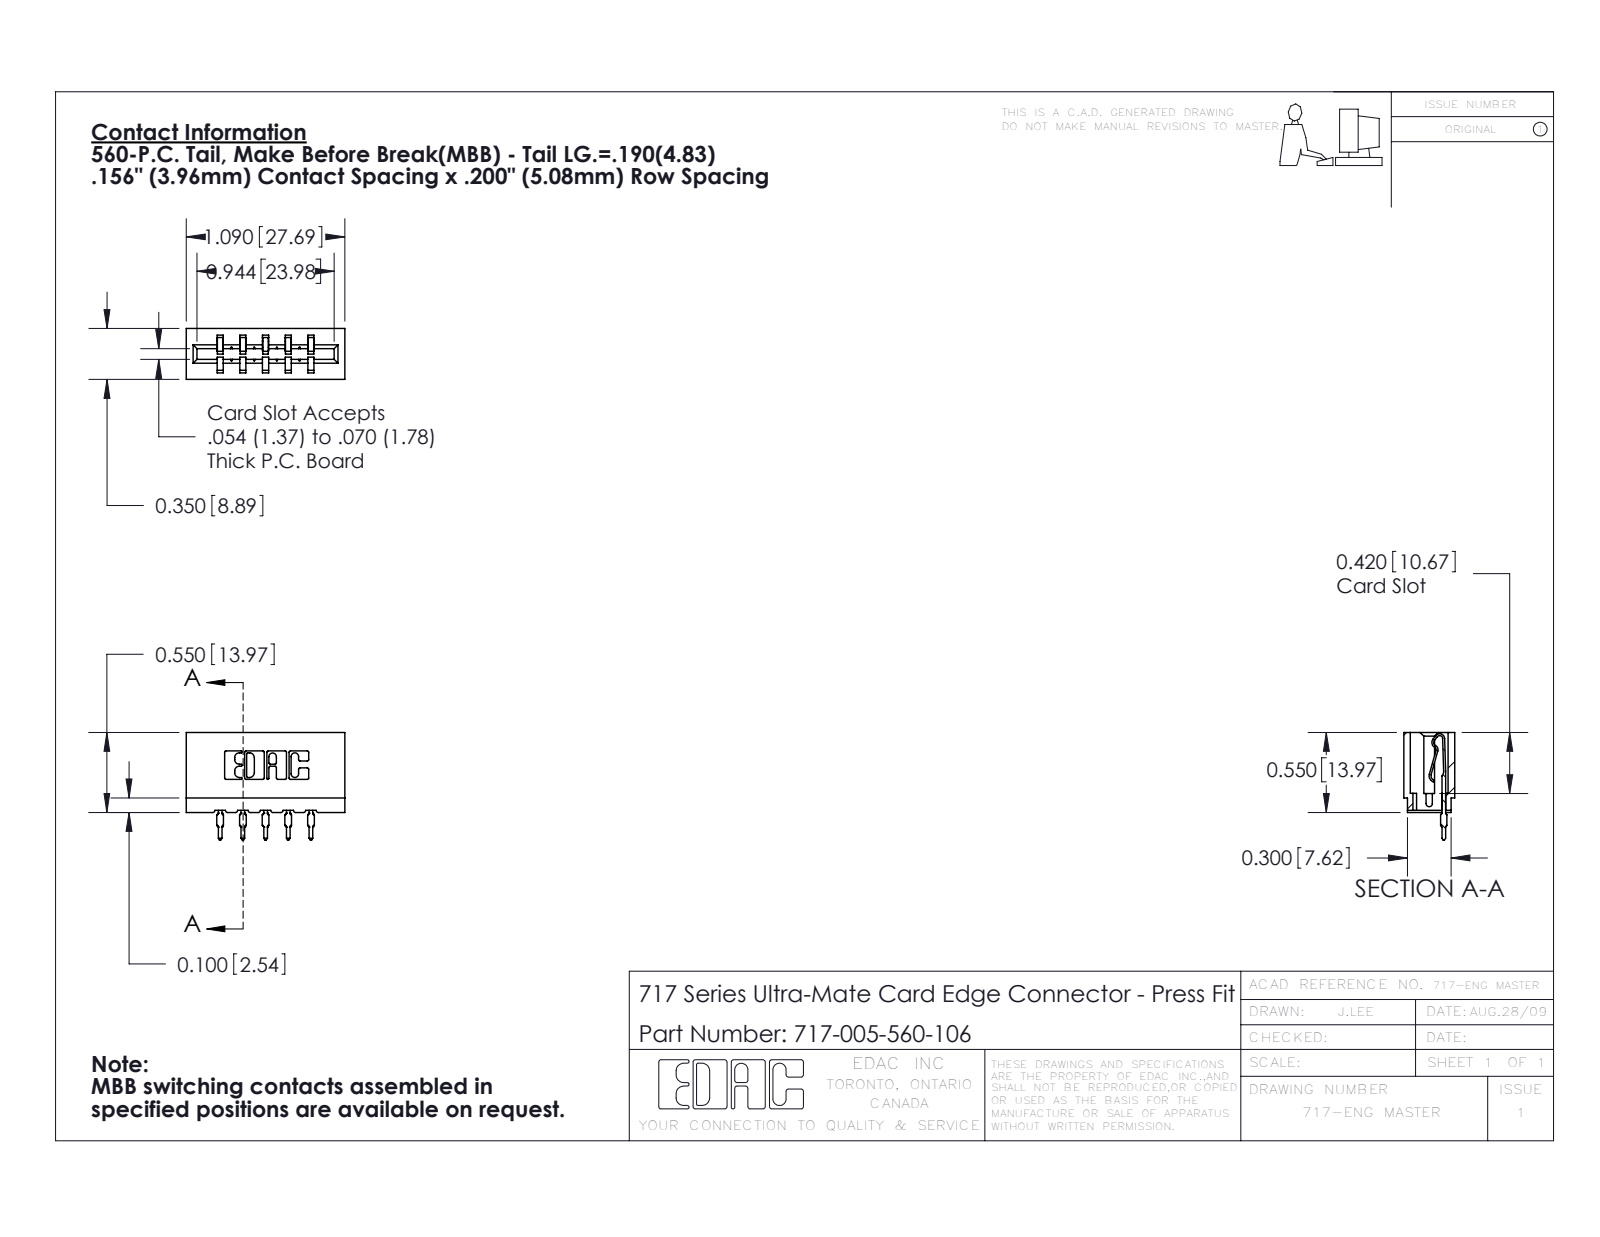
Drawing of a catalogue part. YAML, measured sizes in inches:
part_name: "717 Part_Insulator Option - 06; 717-005-560-106; 745-292-001_560"
step_written_by: "SolidWorks 2016 (CONFIG_CONTROL_DESIGN)"
units: inches
bodies: {solids: 6, faces: 704, planar: 419, cylindrical: 155, other: 130}
overall_size: [1.09, 0.739, 0.35]
volume: 0.154
surface_area: 4.992
partial_cylinders:
  - {radius: 0.01, count: 22}
  - {radius: 0.015, count: 10}
  - {radius: 0.021, count: 10}
  - {radius: 0.007, count: 6}
  - {radius: 0.031, count: 6}
  - {radius: 0.005, count: 4}
  - {radius: 0.011, count: 4}
  - {radius: 0.026, count: 3}
face_to_face_distances: [0.212, 0.156, 0.138, 0.35, 0.198, 0.042, 0.312, 0.312, 0.468, 0.074]
